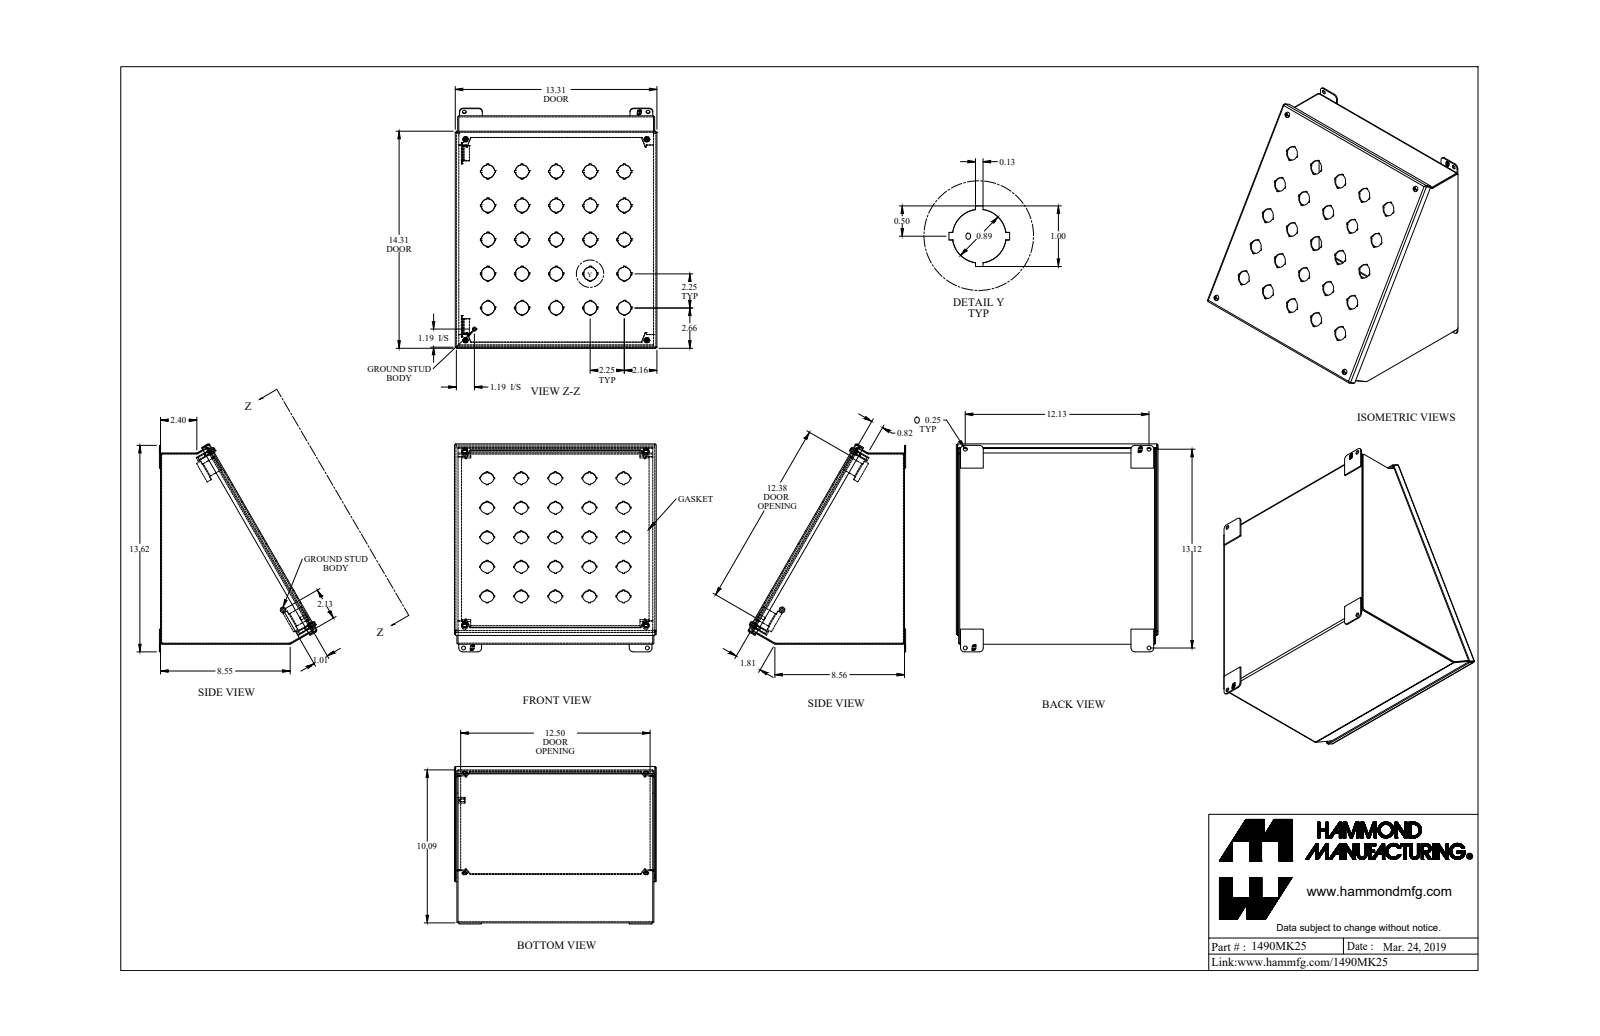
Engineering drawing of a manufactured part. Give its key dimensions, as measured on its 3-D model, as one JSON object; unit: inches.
{"part_name": "1490MK25_Default", "step_written_by": "SolidWorks 2019 (CONFIG_CONTROL_DESIGN)", "units": "inches", "bodies": {"solids": 26, "faces": 1094, "planar": 783, "cylindrical": 273, "other": 38}, "overall_size": [13.737, 13.312, 10.428], "volume_in3": 52.72, "surface_area_in2": 1494, "round_holes": [[0.875, 14], [0.875, 11], [0.25, 8], [0.159, 4], [0.12, 1], [0.136, 1], [0.156, 1]], "round_bosses_or_shafts": [[0.39, 4], [0.275, 4], [0.19, 4], [0.148, 4], [0.375, 1], [0.29, 1]], "partial_cylinders_radius": [[0.108, 18], [0.036, 12], [0.029, 9], [0.086, 9], [0.25, 8], [0.125, 4], [0.16, 4], [0.171, 4]], "face_to_face_distances": [0.072, 0.072, 12.928, 12.856, 13, 12.543, 12.615, 12.472, 0.156, 14.084], "hole_center_spacings": [5.031, 2.25, 3.182, 4.5, 6.75, 7.115, 8.113, 7.115]}
